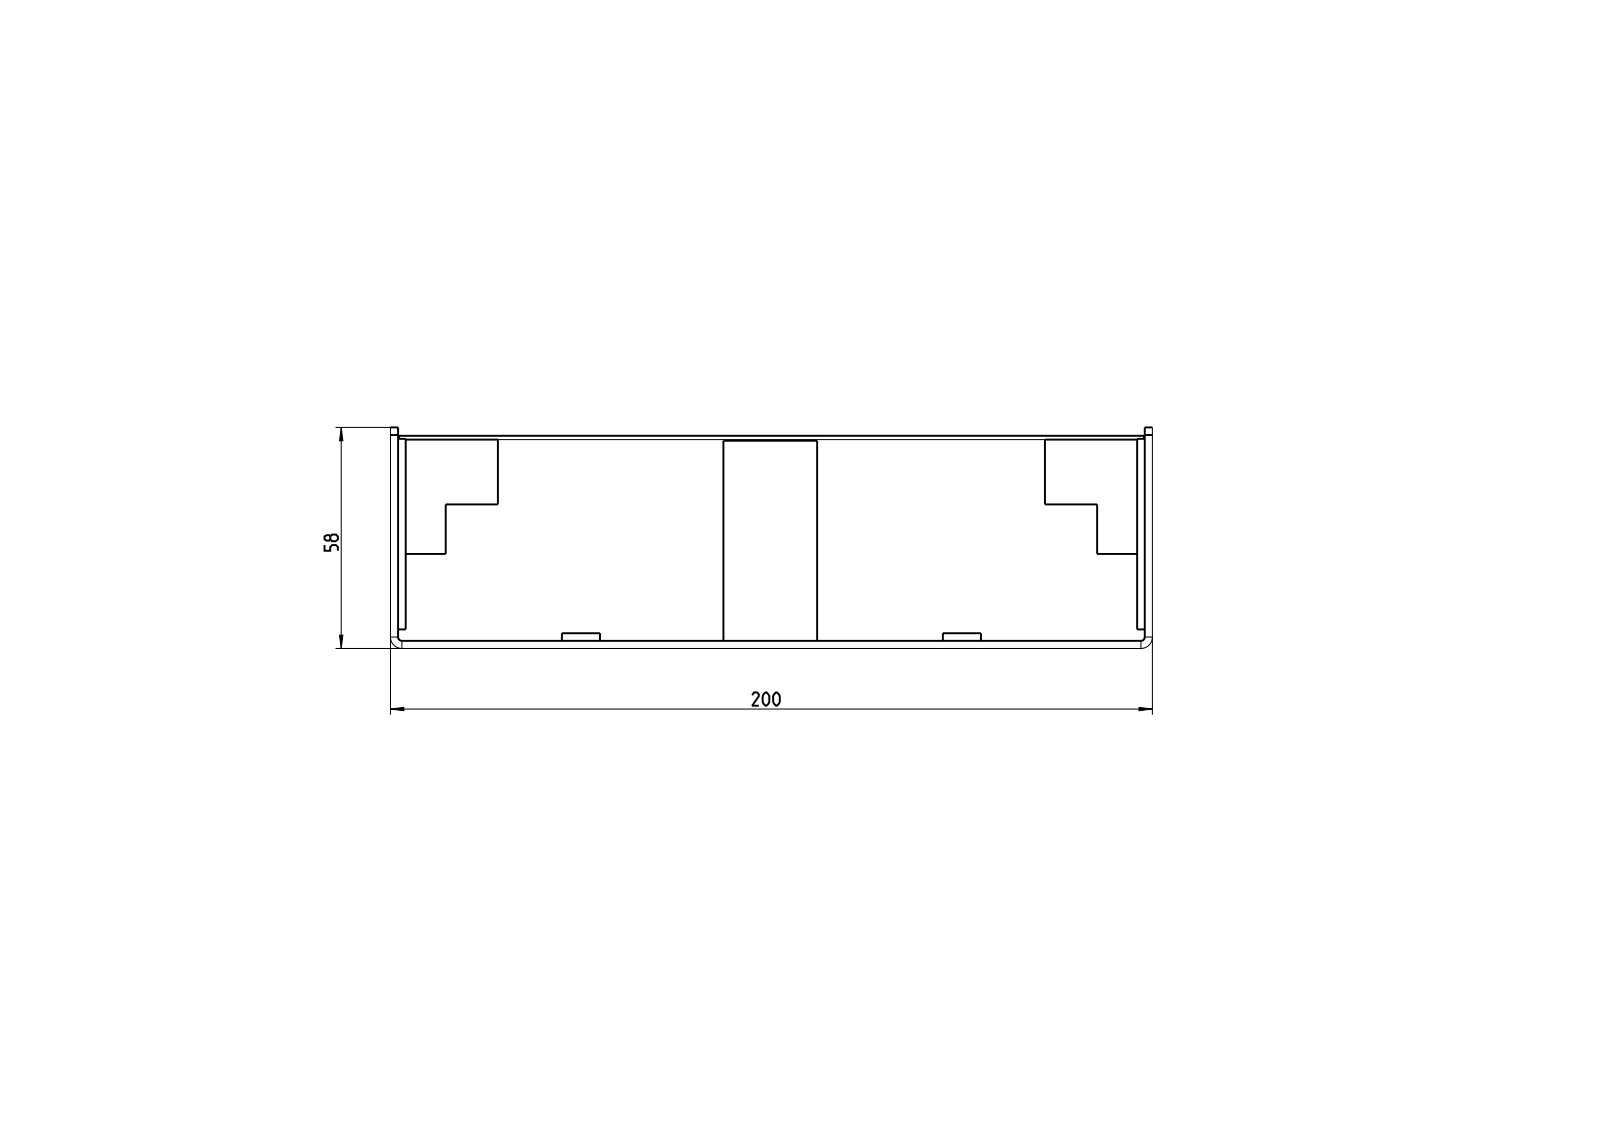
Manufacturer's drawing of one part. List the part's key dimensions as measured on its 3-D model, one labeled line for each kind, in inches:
Part name (STEP PRODUCT): T-01017; T-01024; T-01025_AF0; T-01026_ASM (+6 more)
STEP written by: CREO PARAMETRIC BY PTC INC, 2022024 (AUTOMOTIVE_DESIGN)
Units: inches
Bodies: 12 solids, 337 faces (218 planar, 77 cylindrical, 42 other)
Overall size (bounding box): 78.74 × 7.874 × 2.293
Volume: 343.3 in³ · Surface area: 5 013 in²
Round holes (diameter × count): ⌀0.236 ×8, ⌀0.335 ×8, ⌀0.535 ×5
Round bosses / shafts (diameter × count): ⌀0.394 ×8
Partial cylindrical surfaces — rounded edges, fillets, slot ends (radius × count): R0.004 ×10, R0.039 ×2, R0.118 ×2
Main face-to-face distances: 0.079, 2.079, 7.717, 0.039, 2.118, 2.157, 2.197, 7.638, 0.157, 7.795
Hole centre spacings: 23.622, 23.948, 47.244, 0.787, 3.937, 4.015, 47.408, 22.835
